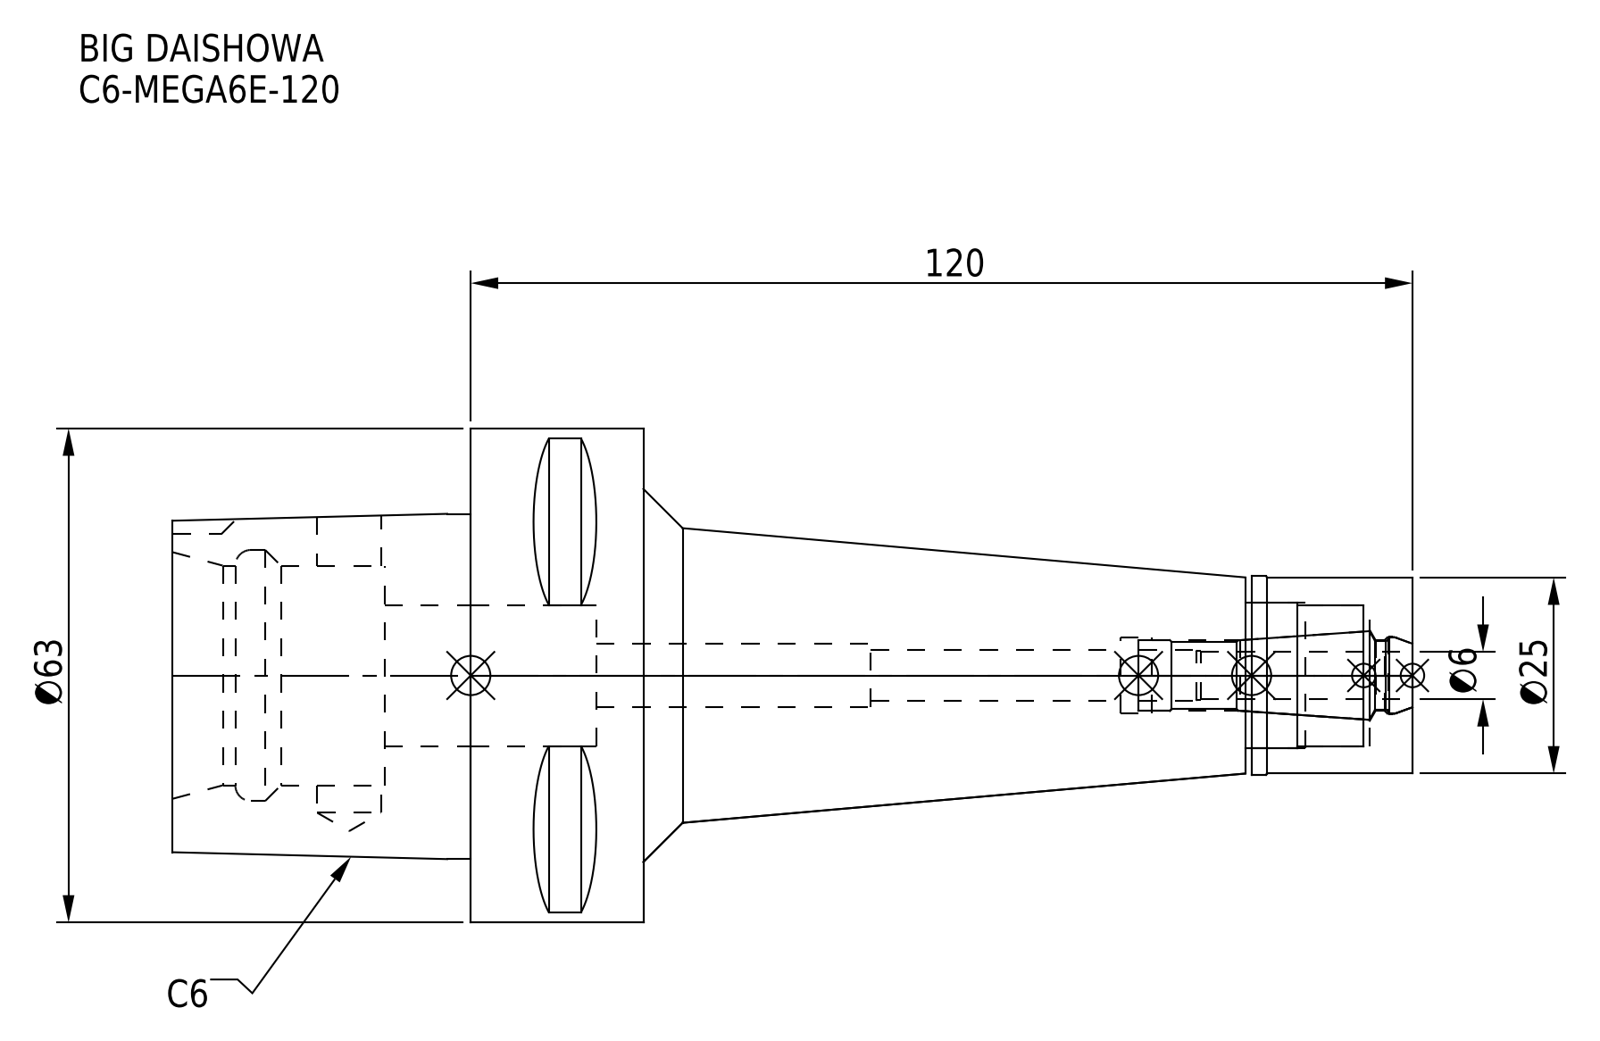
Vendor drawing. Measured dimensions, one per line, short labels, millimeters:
name: MEN6_1.stp; C6-MEGA6E-120-060-FreeParts; C6-MEGA6E-120; DXF_TEMP_ASSY_ASM_4_ASM.stp (+3 more)
written by: SolidWorks 2019 (CONFIG_CONTROL_DESIGN)
unit: mm
bodies: 2 solids, 100 faces (37 planar, 39 cylindrical, 24 other)
size: 158 × 63 × 63
volume: 164 213 mm³; area: 33 621 mm²
holes: 1× ⌀6.4, 1× ⌀8, 1× ⌀8.1, 1× ⌀9, 1× ⌀9.6, 1× ⌀9.9, 1× ⌀18, 1× ⌀18.5, 1× ⌀28, 1× ⌀32
bosses: 1× ⌀63, 1× ⌀25.3, 1× ⌀25
rounds: 1× R5
face distances: 22, 27, 60, 38, 98, 120, 158, 131, 33, 11
